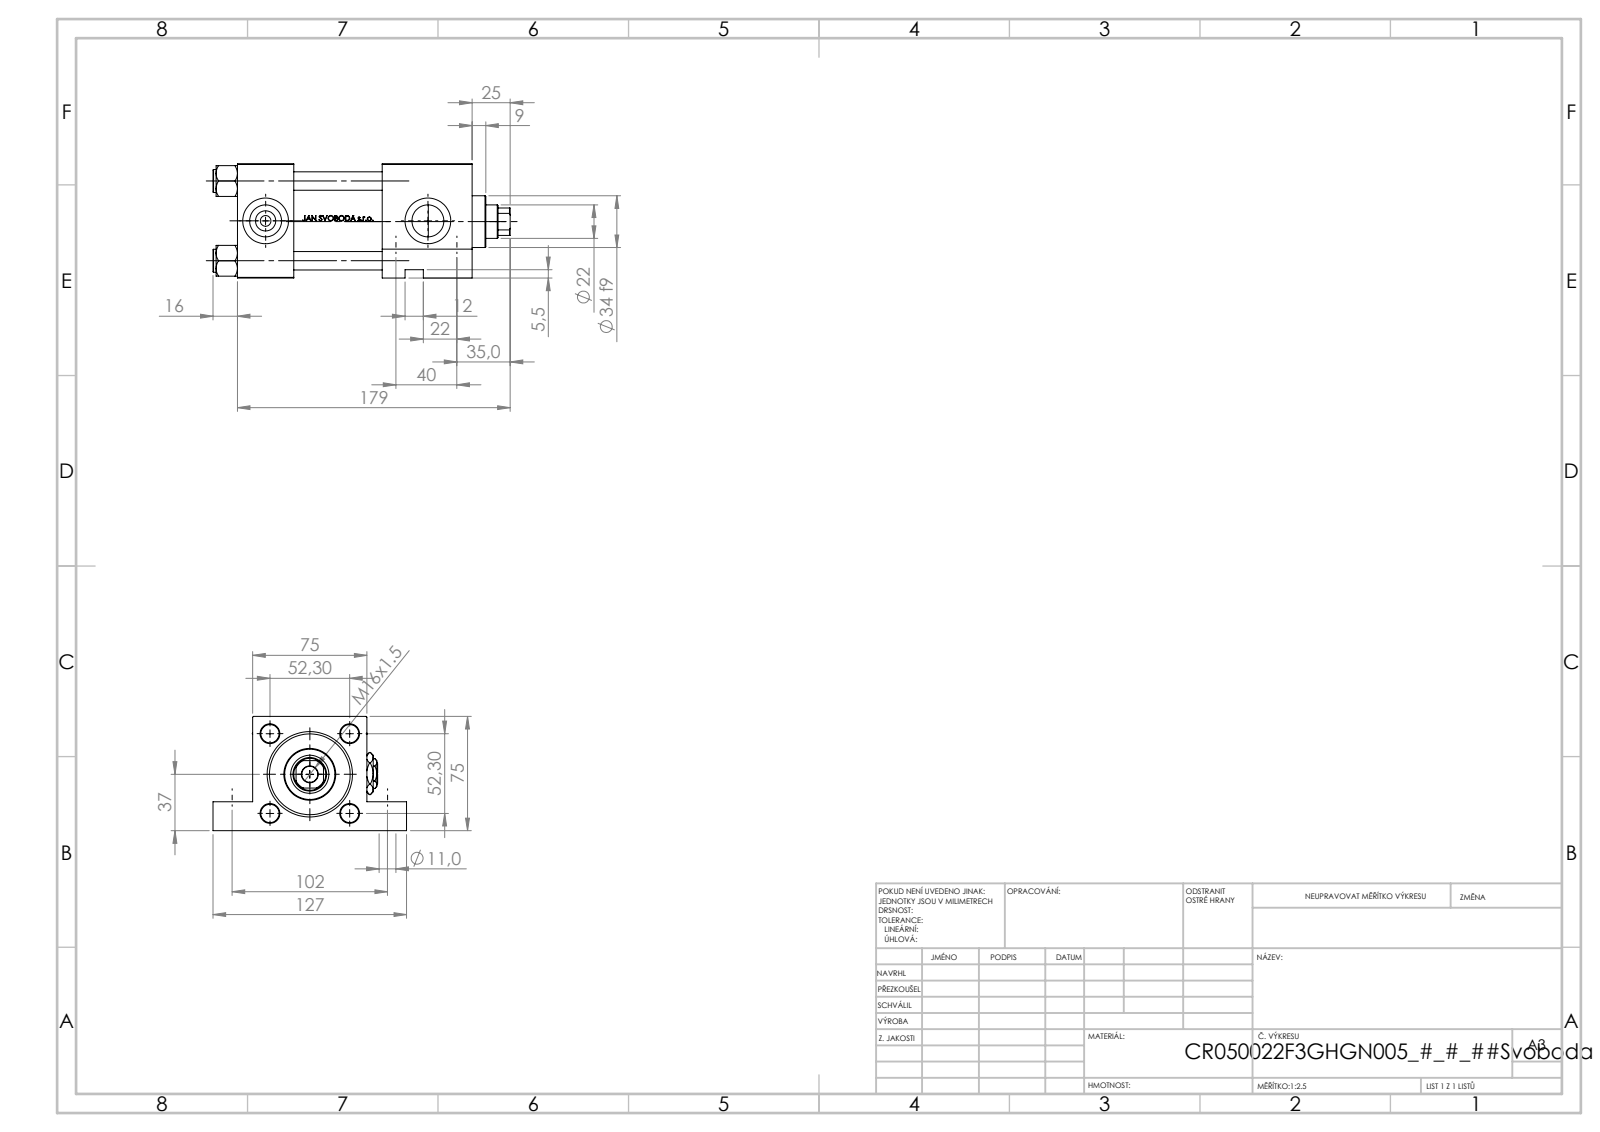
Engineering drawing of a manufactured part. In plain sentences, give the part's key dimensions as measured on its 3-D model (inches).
The part is named "V215CR_VCP_F; V215_VC_A; V215CR_F_TYCINKA; V215CR_F_Body (+2 more)". Its 3-D file was written by "SolidWorks 2019 (CONFIG_CONTROL_DESIGN)". It is 13 solids with 1199 faces: 483 planar, 134 cylindrical and 582 other. Overall it measures 7.677 by 5 by 2.953 inches. Its volume is 42.85 cubic inches and its surface area 248.9 square inches. Round holes: 4 of diameter 0.472, 3 of diameter 0.825, 3 of diameter 1.181, 2 of diameter 0.276, 2 of diameter 0.433, 2 of diameter 0.433, 1 of diameter 0.413, 1 of diameter 0.669, 1 of diameter 0.866, 1 of diameter 0.984, 1 of diameter 1.614, 1 of diameter 1.969. Round bosses or shafts: 4 of diameter 0.591, 1 of diameter 2.205, 1 of diameter 1.339. Partial cylindrical surfaces (rounded edges, fillets, slot ends): 1 of radius 0.413. The main face-to-face distances are 2.953, 1.457, 6.063, 4.606, 3.74, 2.283, 2.323, 0.748, 2.205, 4.933. The hole center spacings are 2.059, 1.442, 1.47, 1.575, 2.912, 4.016, 4.313, 0.512.
